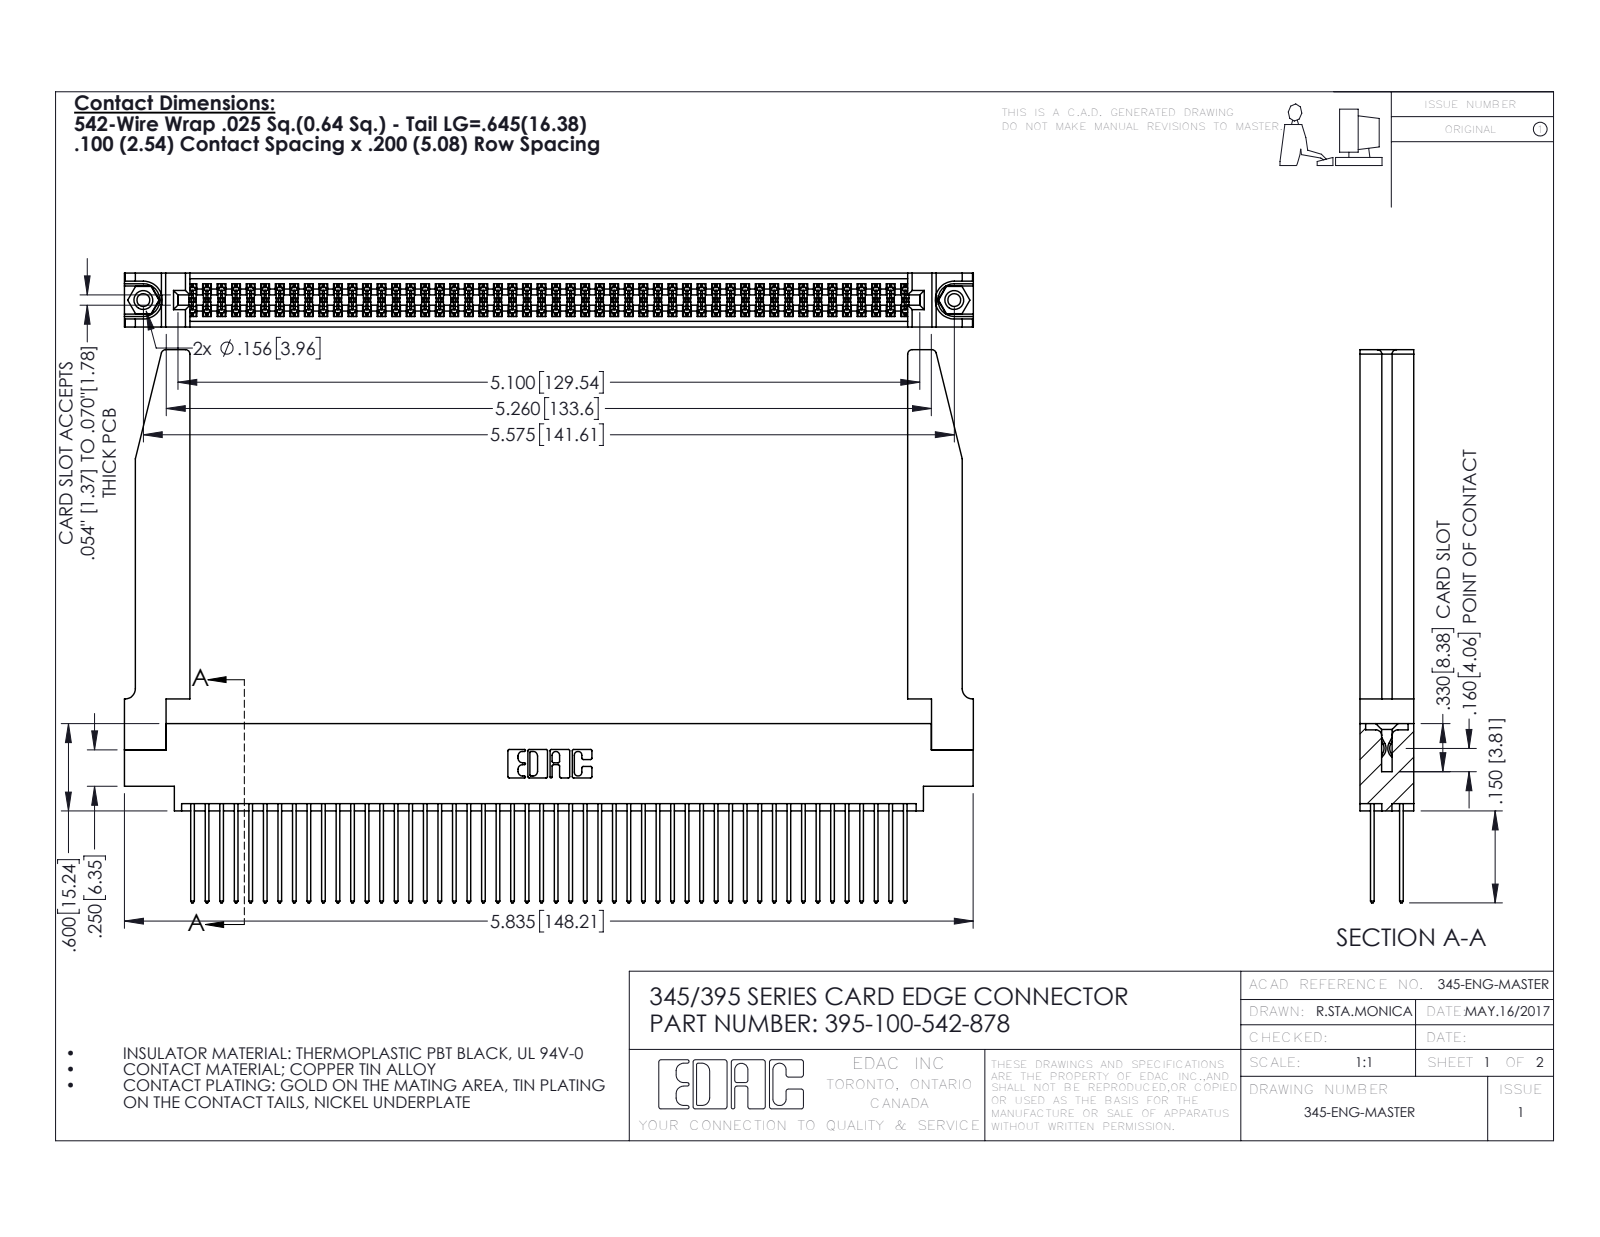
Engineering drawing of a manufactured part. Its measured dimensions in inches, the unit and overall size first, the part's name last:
Units: inches
Overall size (bounding box): 5.836 × 3.802 × 0.37
Round holes (diameter × count): ⌀0.089 ×2, ⌀0.125 ×2, ⌀0.156 ×2, ⌀0.064 ×1
Round bosses / shafts (diameter × count): ⌀0.155 ×2
Partial cylindrical surfaces — rounded edges, fillets, slot ends (radius × count): R0.006 ×150, R0.01 ×100, R0.01 ×22, R0.03 ×8, R0.007 ×6, R0.031 ×6, R0.026 ×3, R0.014 ×2
Main face-to-face distances: 0.072, 0.298, 0.37, 0.098, 0.272, 0.025, 0.2, 0.225, 0.175, 0.15
Hole centre spacings: 0.27, 5.339, 5.575
Volume: 1.379 in³ · Surface area: 48.41 in²
Bodies: 105 solids, 5364 faces (3526 planar, 1786 cylindrical, 52 other)
Part name (STEP PRODUCT): 345-250-001_345-250-001-102; 345 Part_0.170 Offset - 0.156 Dia-TH; 345-292-001_345-293-142; 345-220-078_345-220-078 (+1 more)
STEP written by: SolidWorks 2016 (CONFIG_CONTROL_DESIGN)
